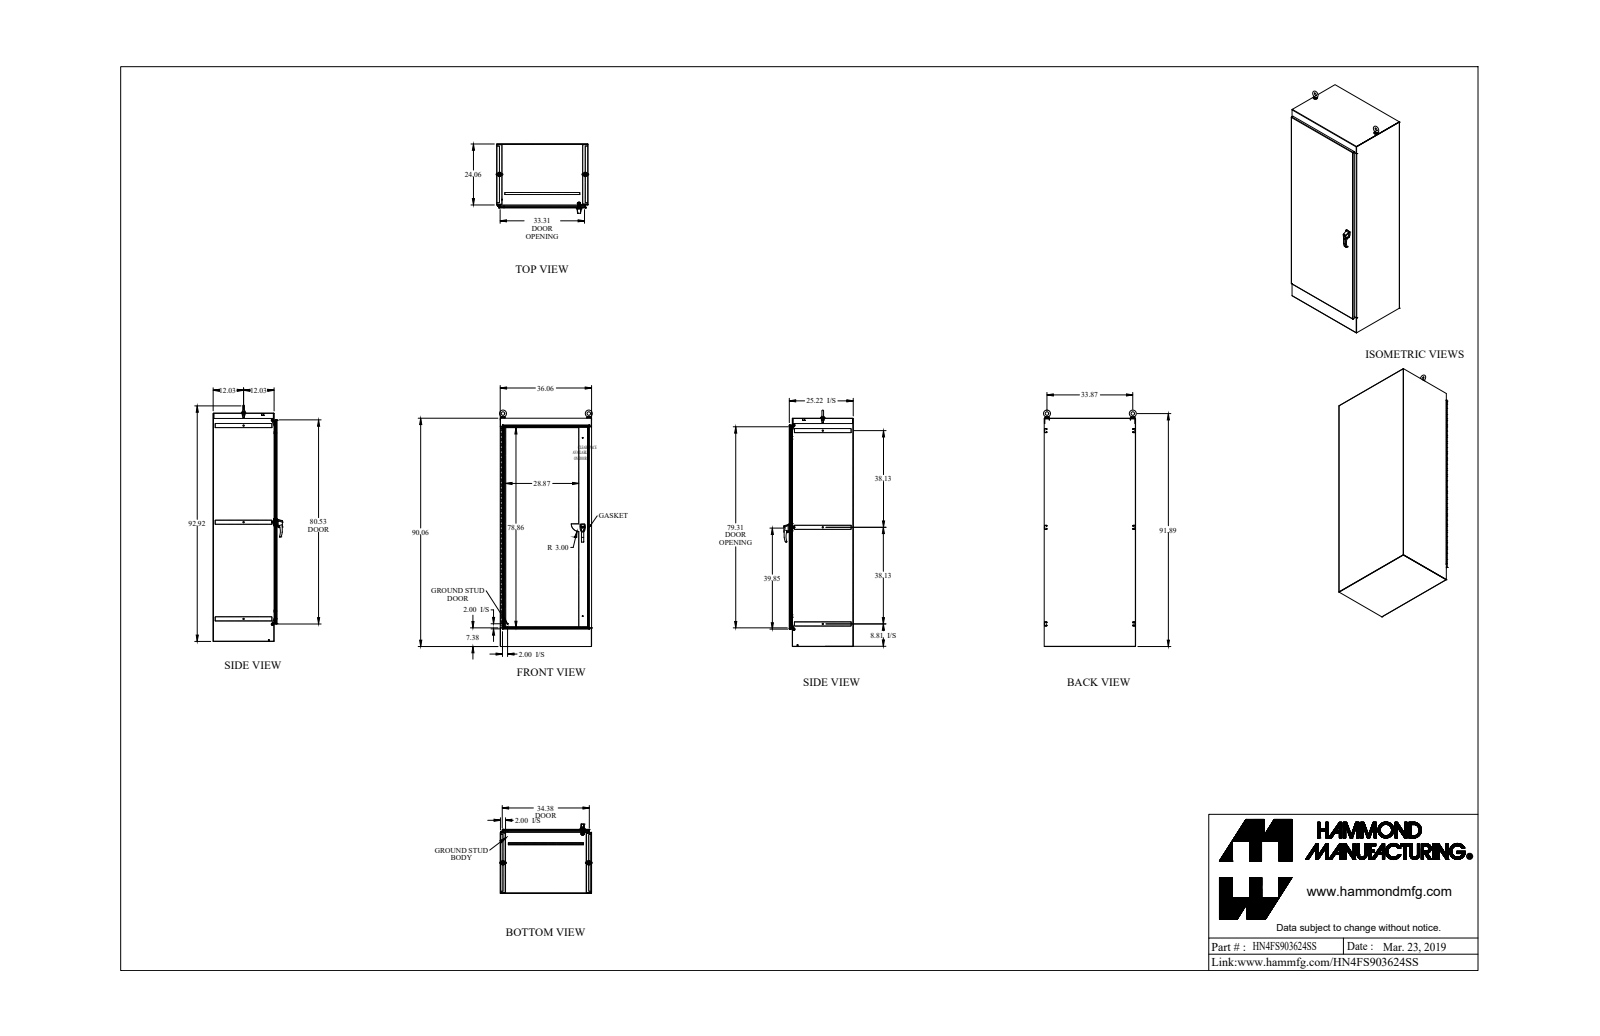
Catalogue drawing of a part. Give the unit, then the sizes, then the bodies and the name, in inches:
Units: inches
Overall size (bounding box): 93.489 × 36.604 × 27.362
Round holes (diameter × count): ⌀0.304 ×13, ⌀0.35 ×7, ⌀0.5 ×3, ⌀0.25 ×2, ⌀0.257 ×2, ⌀0.28 ×2, ⌀0.281 ×2, ⌀0.313 ×2, ⌀0.39 ×2, ⌀0.413 ×2, ⌀0.527 ×2, ⌀0.625 ×2
Round bosses / shafts (diameter × count): ⌀1.75 ×2, ⌀1.5 ×2, ⌀1.25 ×2, ⌀1 ×2, ⌀0.75 ×2, ⌀0.738 ×2, ⌀0.63 ×2, ⌀0.625 ×2
Partial cylindrical surfaces — rounded edges, fillets, slot ends (radius × count): R0.043 ×42, R0.138 ×36, R0.5 ×23, R0.125 ×22, R0.018 ×16, R0.06 ×15, R0.048 ×14, R0.143 ×14
Main face-to-face distances: 0.095, 25.152, 35.965, 25.057, 25.247, 35.87, 36.06, 89.965, 23.965, 1.187
Hole centre spacings: 6, 12, 18, 24, 30, 36, 42, 48
Volume: 1 401 in³ · Surface area: 29 545 in²
Bodies: 54 solids, 2048 faces (934 planar, 949 cylindrical, 165 other)
Part name (STEP PRODUCT): HN4FS903624SS
STEP written by: SolidWorks 2018 (AUTOMOTIVE_DESIGN)
